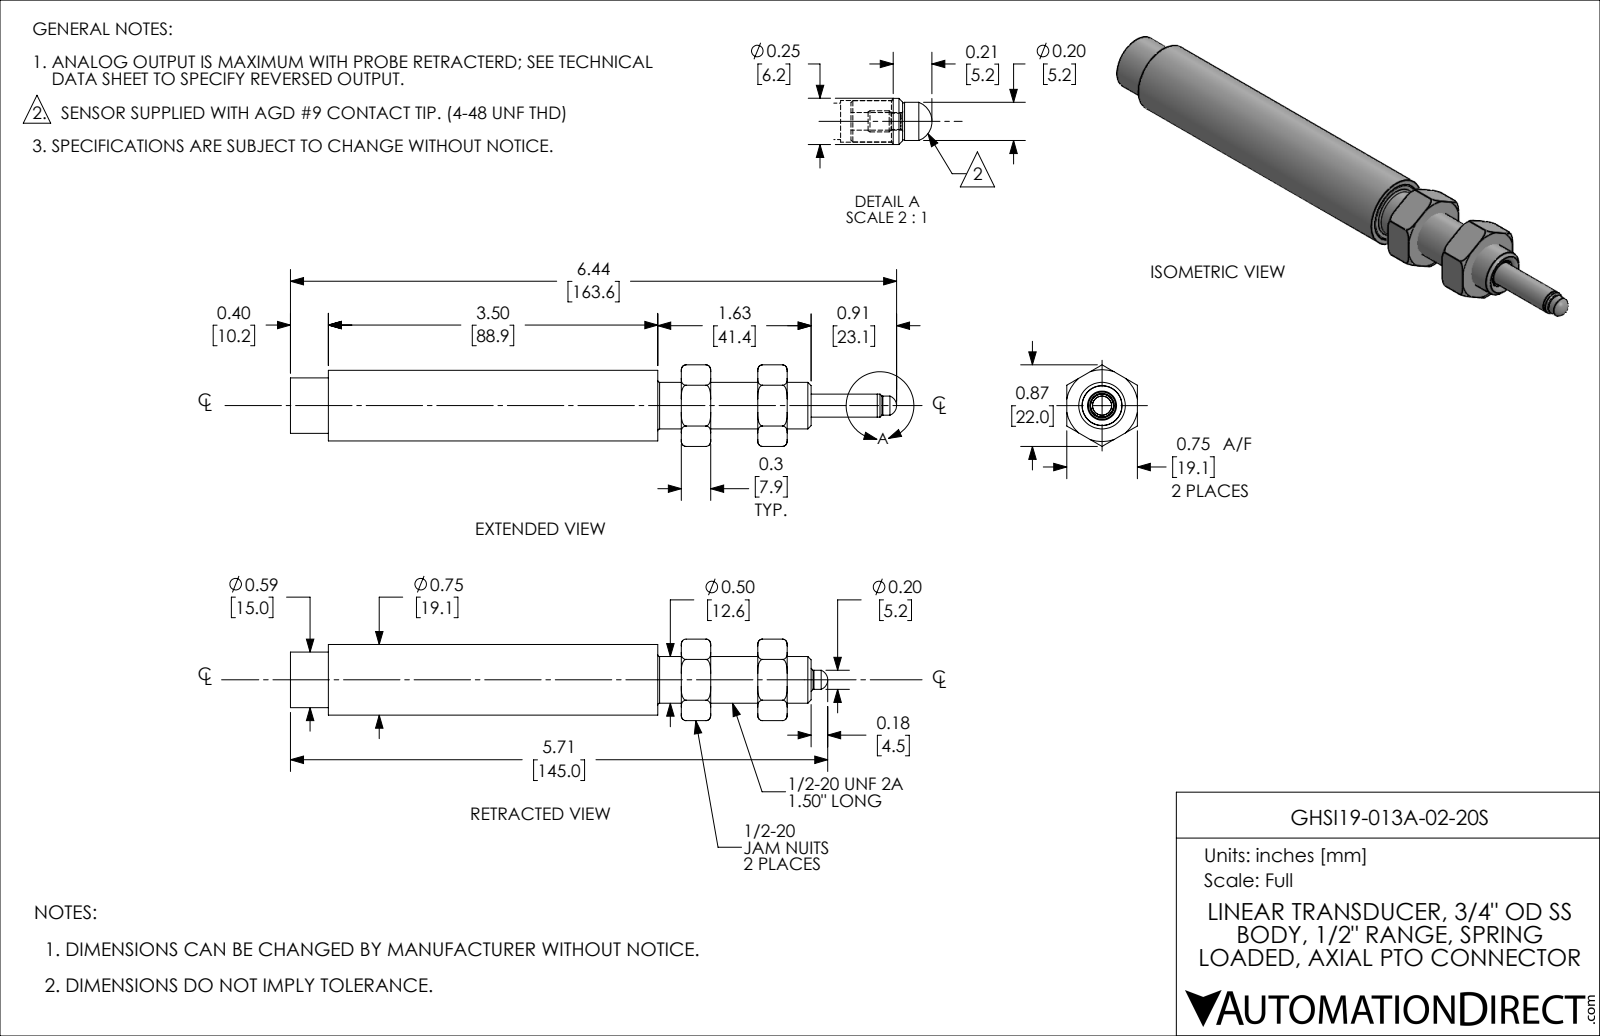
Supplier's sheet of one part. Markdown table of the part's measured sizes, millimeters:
| quantity | value |
| --- | --- |
| part name | GHSI19-013A-02-20S |
| STEP written by | SolidWorks 2019 (AUTOMOTIVE_DESIGN) |
| units | millimeters |
| bodies | 11 solids, 187 faces (77 planar, 65 cylindrical, 45 other) |
| overall size | 145 × 22 × 19.1 |
| volume | 19 570 mm³ |
| surface area | 23 620 mm² |
| round holes (diameter × count) | 2.4 × 1, 4 × 1, 4.9 × 1, 5.6 × 1, 6.3 × 1, 7.7 × 1, 7.9 × 1, 11.5 × 1, 13.2 × 1, 15.7 × 1, 15.9 × 1, 16.5 × 1 |
| round bosses / shafts (diameter × count) | 0.8 × 6, 19.1 × 1, 18.4 × 1, 17.1 × 1, 15.8 × 1, 15 × 1, 12.6 × 1, 9.5 × 1 |
| partial cylindrical surfaces (radius × count) | 0.3 × 2, 1 × 2, 3.4 × 1, 4 × 1, 7 × 1 |
| main face-to-face distances | 19.1, 20.6, 8, 20.7, 28.6, 12.7, 7.9, 19.1, 95.8, 103.8 |
